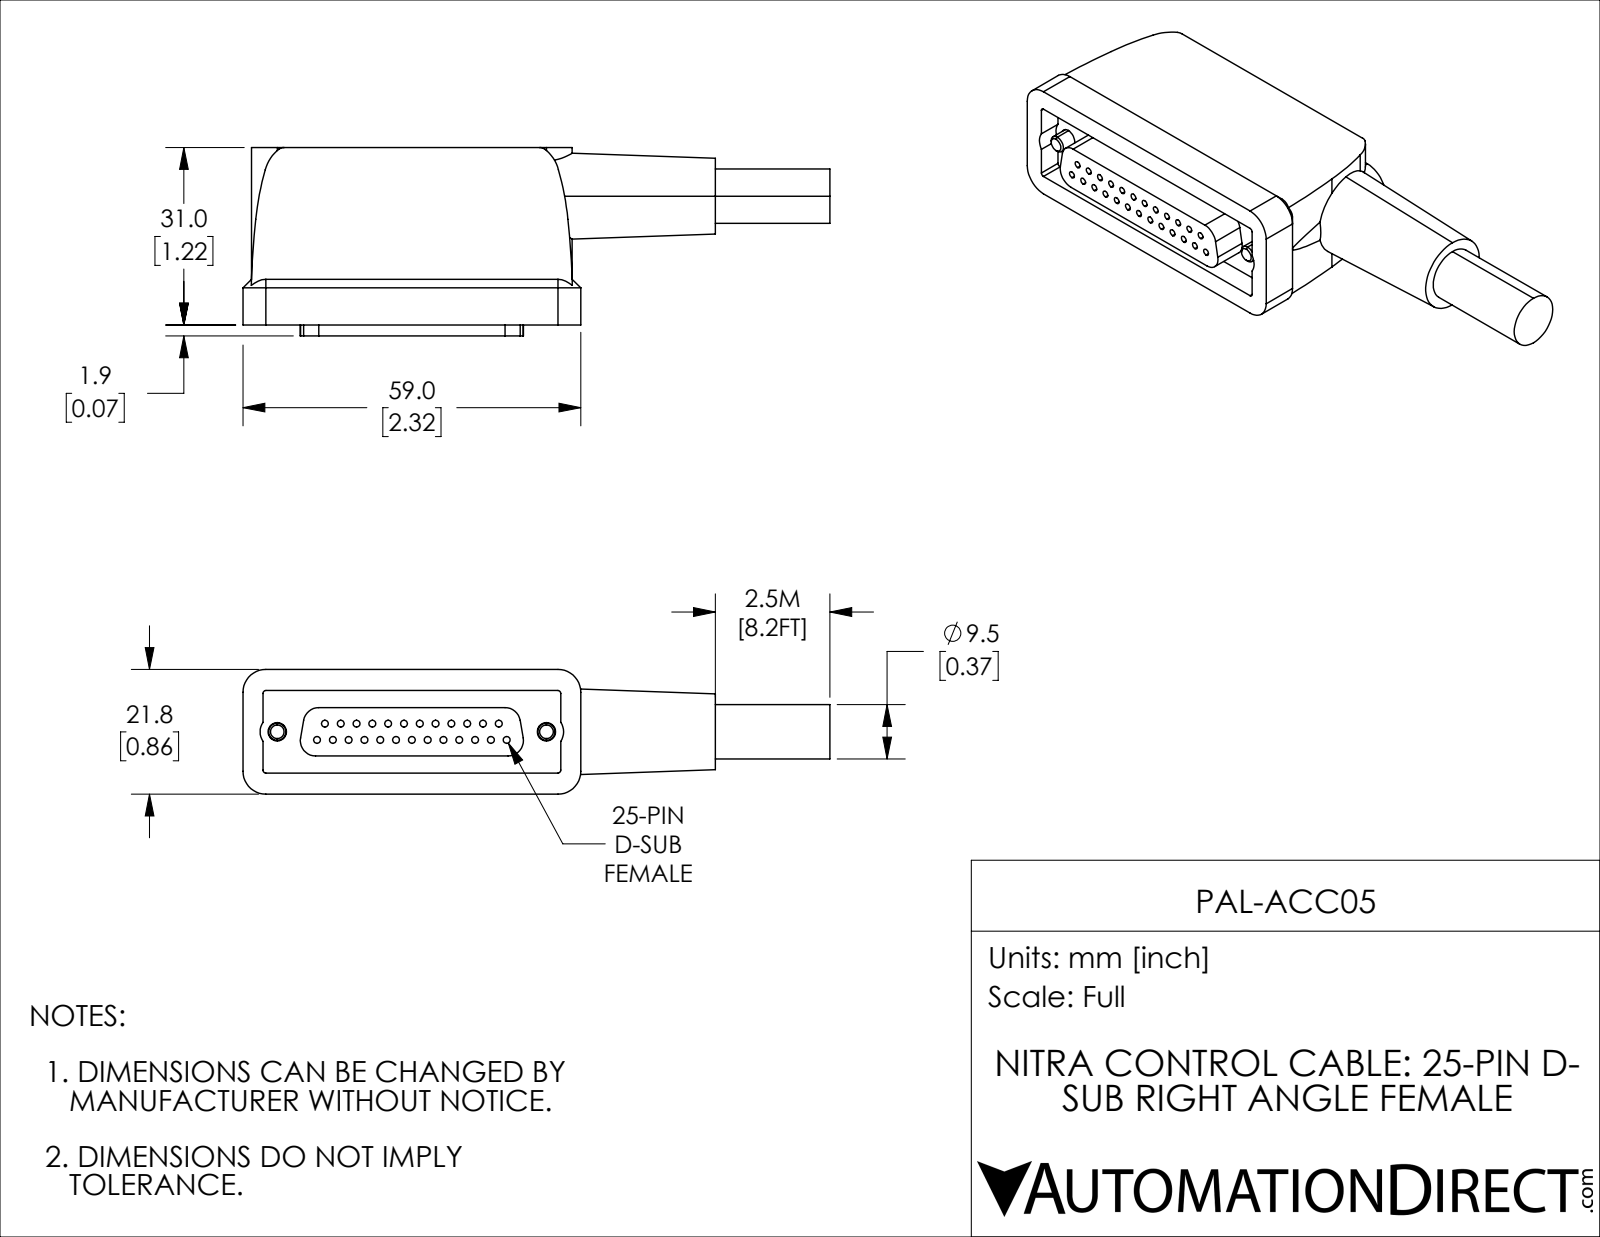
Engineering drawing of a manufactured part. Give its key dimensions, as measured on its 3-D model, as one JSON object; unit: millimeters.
{"part_name": "PAL-ACC05", "step_written_by": "SolidWorks 2019 (CONFIG_CONTROL_DESIGN)", "units": "millimeters", "bodies": {"solids": 1, "faces": 186, "planar": 71, "cylindrical": 101, "other": 14}, "overall_size": [102.5, 32.9, 21.8], "volume_mm3": 37542, "surface_area_mm2": 11486, "round_holes": [[1.2, 25], [3.2, 2], [5, 2]], "round_bosses_or_shafts": [[4.6, 2], [3, 2], [9.5, 1]], "partial_cylinders_radius": [[0.5, 4], [2.68, 4], [4, 4], [1.4, 2], [3, 2], [4.5, 2], [6.5, 2], [50, 2]], "face_to_face_distances": [18.8, 1.5, 20.3, 31, 4.1, 26.9, 3.7, 18.1, 2.2, 16.6], "hole_center_spacings": [3.16, 2.76, 5.02, 5.52, 7.46, 8.28, 10.07, 11.04]}
